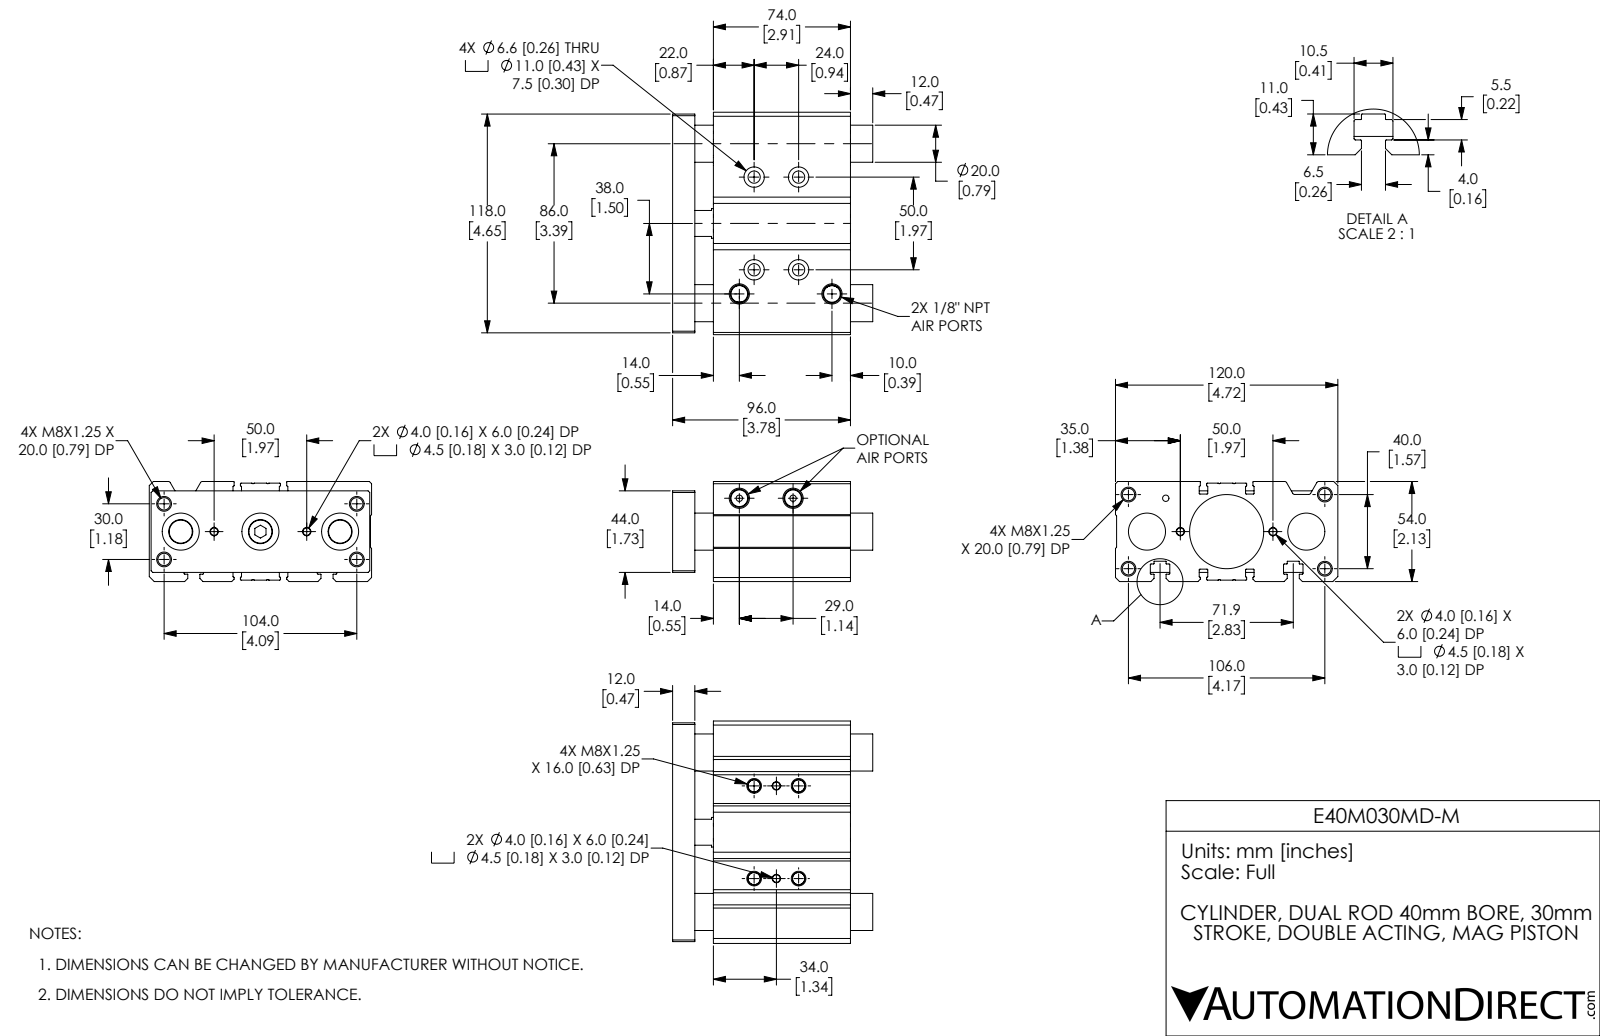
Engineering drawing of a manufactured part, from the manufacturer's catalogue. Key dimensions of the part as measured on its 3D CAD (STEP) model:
Part name (STEP PRODUCT): E40M030MD-M_BODY; E40M030MD-M_ENDPLATE; E40M030MD-M
STEP written by: SolidWorks 2019 (CONFIG_CONTROL_DESIGN)
Units: millimetres
Bodies: 5 solids, 427 faces (139 planar, 194 cylindrical, 94 other)
Overall size (bounding box): 120 × 108 × 54
Volume: 469 618 mm³ · Surface area: 113 352 mm²
Round holes (diameter × count): ⌀6.65 ×12, ⌀4 ×4, ⌀4.5 ×4, ⌀6.6 ×4, ⌀11 ×4, ⌀10 ×3, ⌀20 ×3, ⌀3.43 ×2, ⌀10.91 ×2, ⌀12.95 ×2, ⌀3.43 ×1, ⌀20 ×1
Round bosses / shafts (diameter × count): ⌀16 ×1, ⌀12.95 ×1
Partial cylindrical surfaces — rounded edges, fillets, slot ends (radius × count): R0.2 ×32, R0.4 ×28, R1.2 ×4, R0.3 ×2
Main face-to-face distances: 54, 12, 96, 22, 10, 84, 74, 79, 4.15, 48.15
Hole centre spacings: 50, 5.1, 12, 17.49, 22.36, 30.89, 34.41, 35.01
